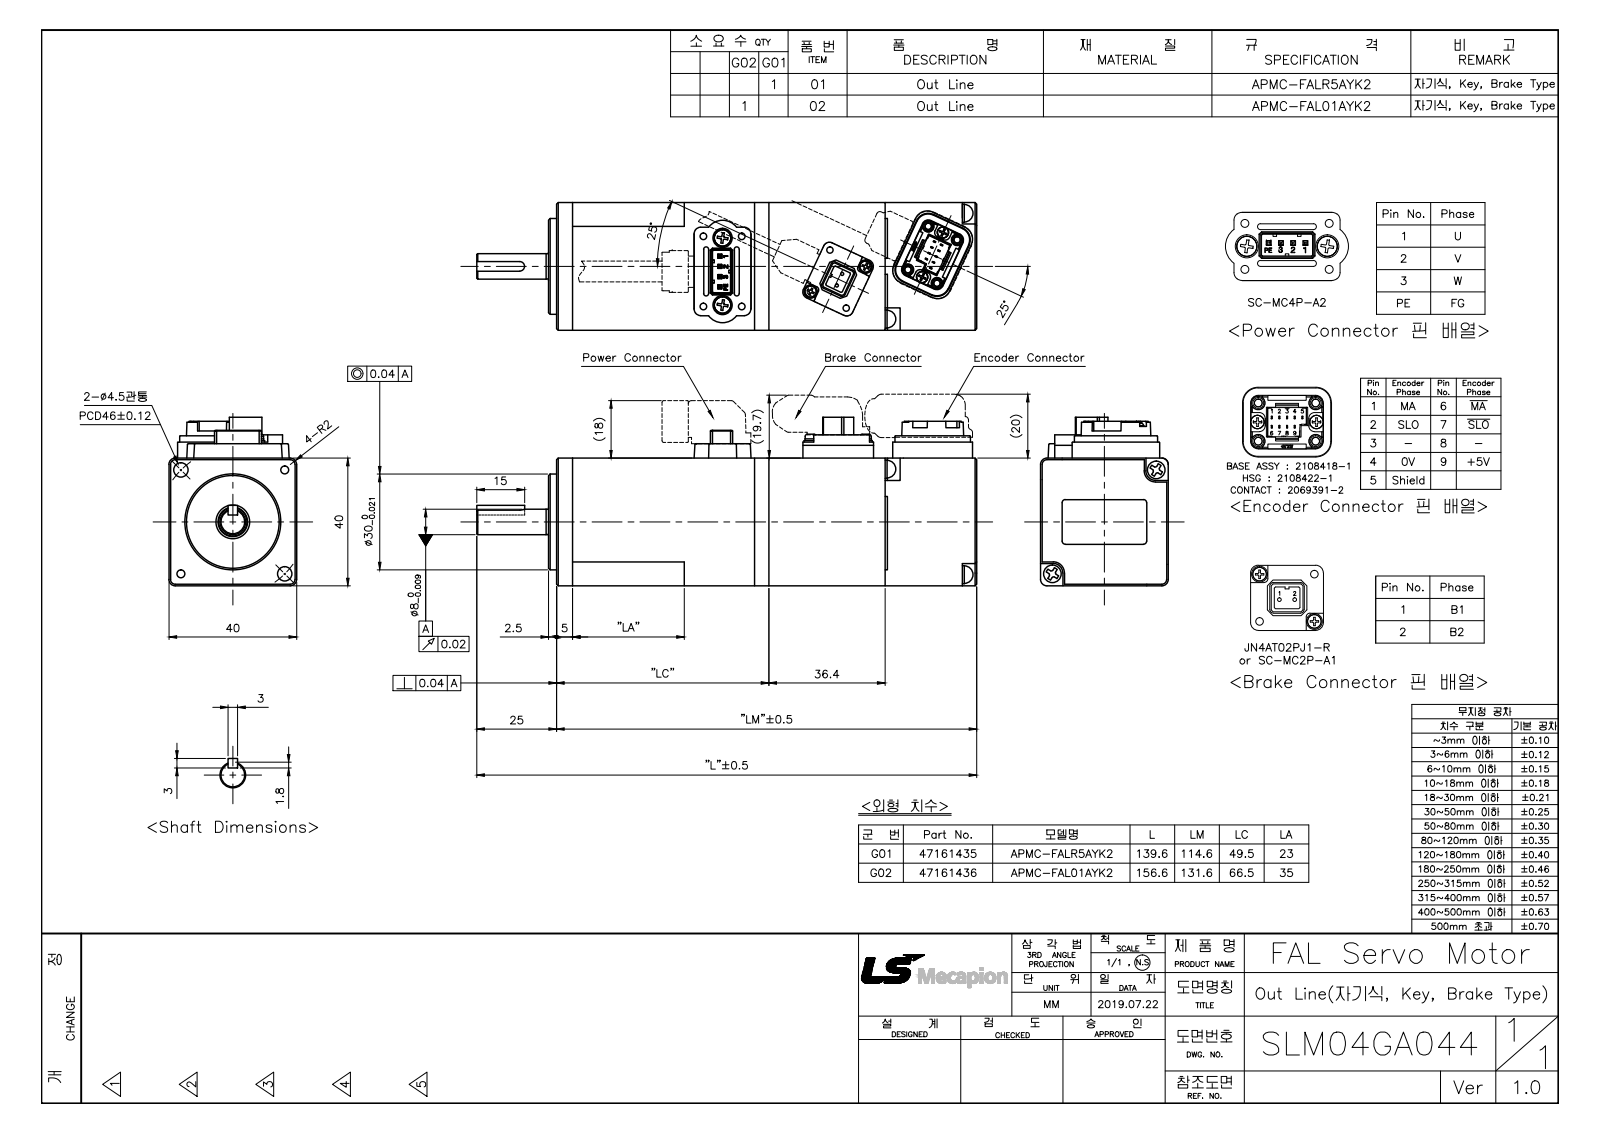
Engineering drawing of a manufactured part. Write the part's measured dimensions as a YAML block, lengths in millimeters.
part_name: "APMC-FALR5AM8K2"
step_written_by: "SolidWorks 2011 (AUTOMOTIVE_DESIGN)"
units: millimeters
bodies: {solids: 34, faces: 1521, planar: 988, cylindrical: 350, other: 183}
overall_size: [139.6, 52.8, 40]
volume: 189600
surface_area: 51957
round_holes:
  - {diameter: 2.1, count: 10}
  - {diameter: 2, count: 6}
  - {diameter: 3, count: 6}
  - {diameter: 3.6, count: 4}
  - {diameter: 1, count: 2}
  - {diameter: 2.2, count: 2}
  - {diameter: 2.5, count: 2}
  - {diameter: 4.5, count: 2}
  - {diameter: 6, count: 2}
  - {diameter: 3.3, count: 1}
  - {diameter: 3.4, count: 1}
  - {diameter: 10.6, count: 1}
round_bosses_or_shafts:
  - {diameter: 5.4, count: 6}
  - {diameter: 4.2, count: 2}
  - {diameter: 3.6, count: 2}
  - {diameter: 3.5, count: 2}
  - {diameter: 0.9, count: 2}
  - {diameter: 30, count: 1}
  - {diameter: 9.8, count: 1}
  - {diameter: 9.5, count: 1}
partial_cylinders:
  - {radius: 0.2, count: 20}
  - {radius: 1, count: 10}
  - {radius: 0.15, count: 9}
  - {radius: 2, count: 8}
  - {radius: 0.45, count: 7}
  - {radius: 1.5, count: 7}
  - {radius: 0.11, count: 6}
  - {radius: 0.3, count: 4}
face_to_face_distances: [40, 4.5, 44.5, 40.9, 0.7, 36.4, 80.9, 37.1, 41.6, 81.6]
hole_center_spacings: [6.02, 9.43, 16, 22.32, 23, 32.52, 2.06, 5]
